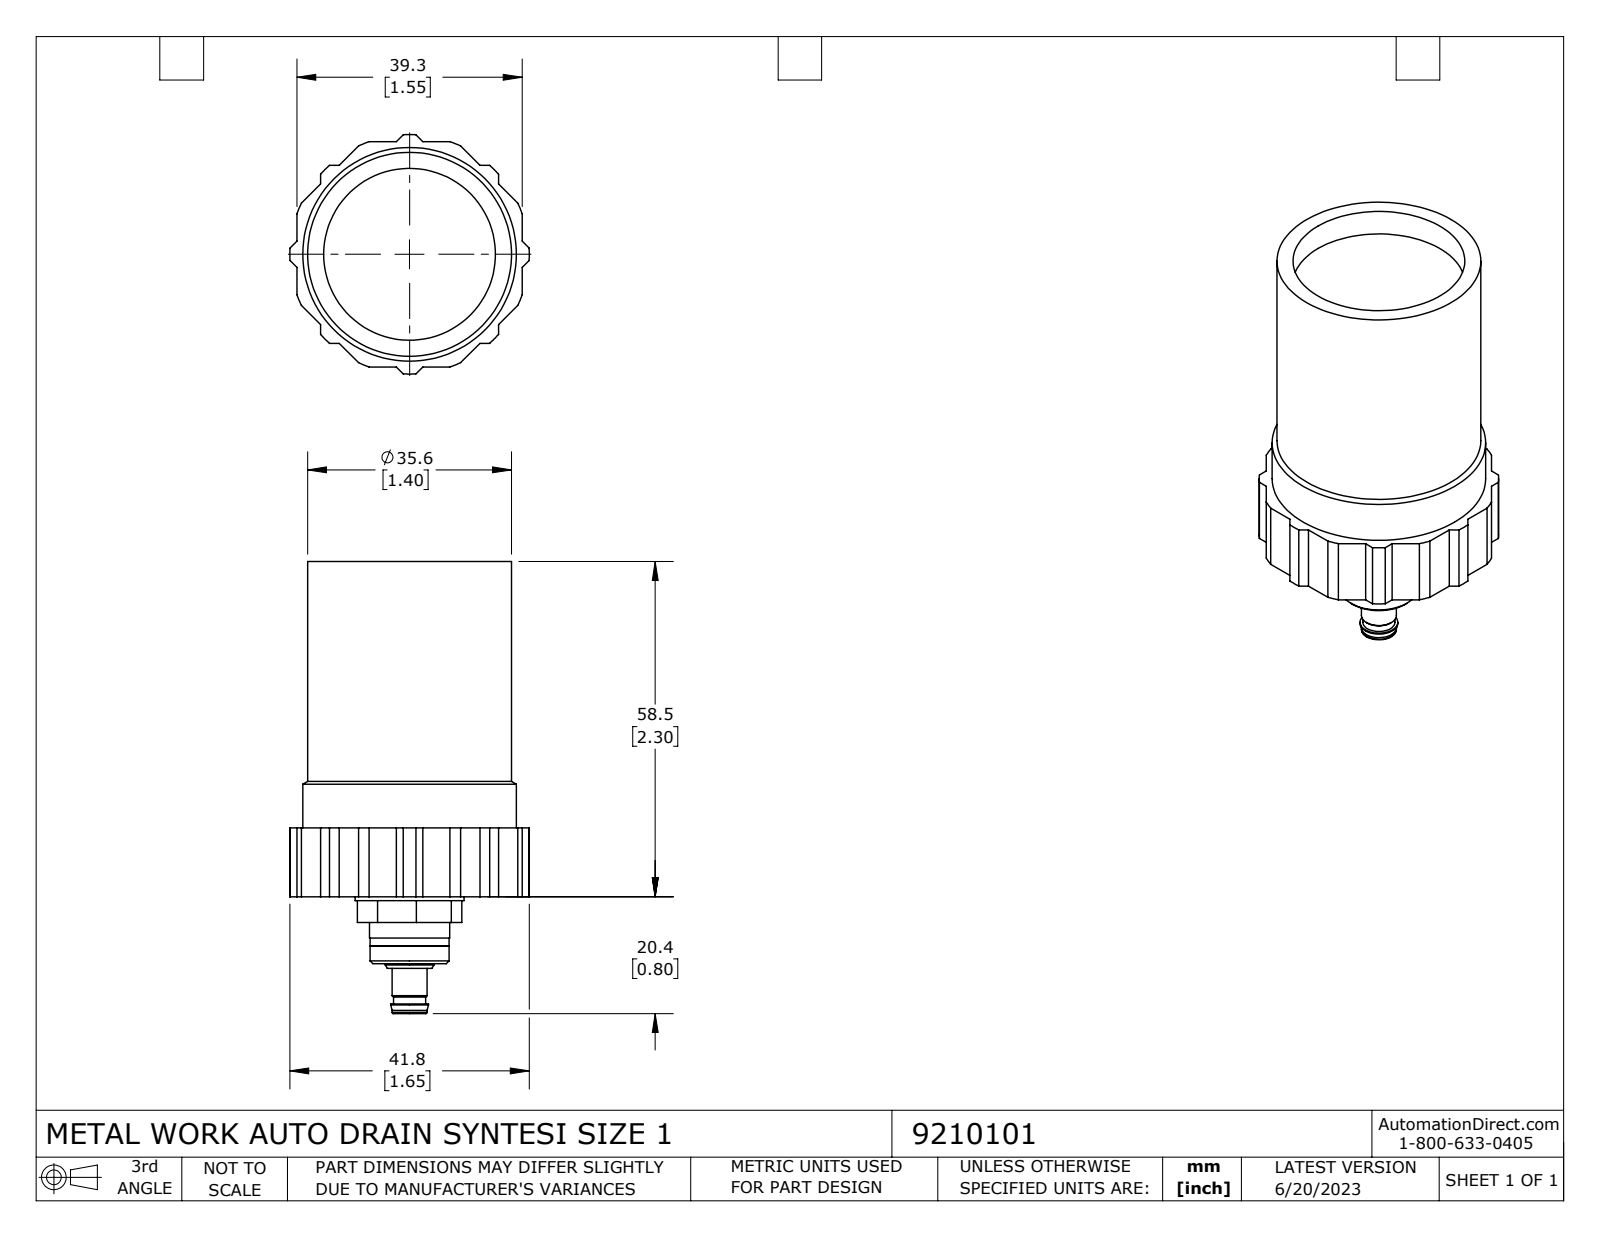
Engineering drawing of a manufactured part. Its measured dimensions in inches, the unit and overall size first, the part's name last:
Units: inches
Overall size (bounding box): 3.106 × 1.646 × 1.646
Round holes (diameter × count): ⌀0.177 ×1, ⌀1.181 ×1
Round bosses / shafts (diameter × count): ⌀1.469 ×1, ⌀1.402 ×1, ⌀0.748 ×1, ⌀0.543 ×1, ⌀0.335 ×1, ⌀0.26 ×1, ⌀0.24 ×1, ⌀0.22 ×1
Partial cylindrical surfaces — rounded edges, fillets, slot ends (radius × count): R0.313 ×1, R0.823 ×1
Main face-to-face distances: 2.114, 1.549, 0.339, 2.453, 2.642, 2.303, 0.189, 0.811, 0.472, 1.642
Volume: 3.788 in³ · Surface area: 18.98 in²
Bodies: 4 solids, 118 faces (57 planar, 43 cylindrical, 18 other)
Part name (STEP PRODUCT): 9210101
STEP written by: SolidWorks 2021 (CONFIG_CONTROL_DESIGN)
